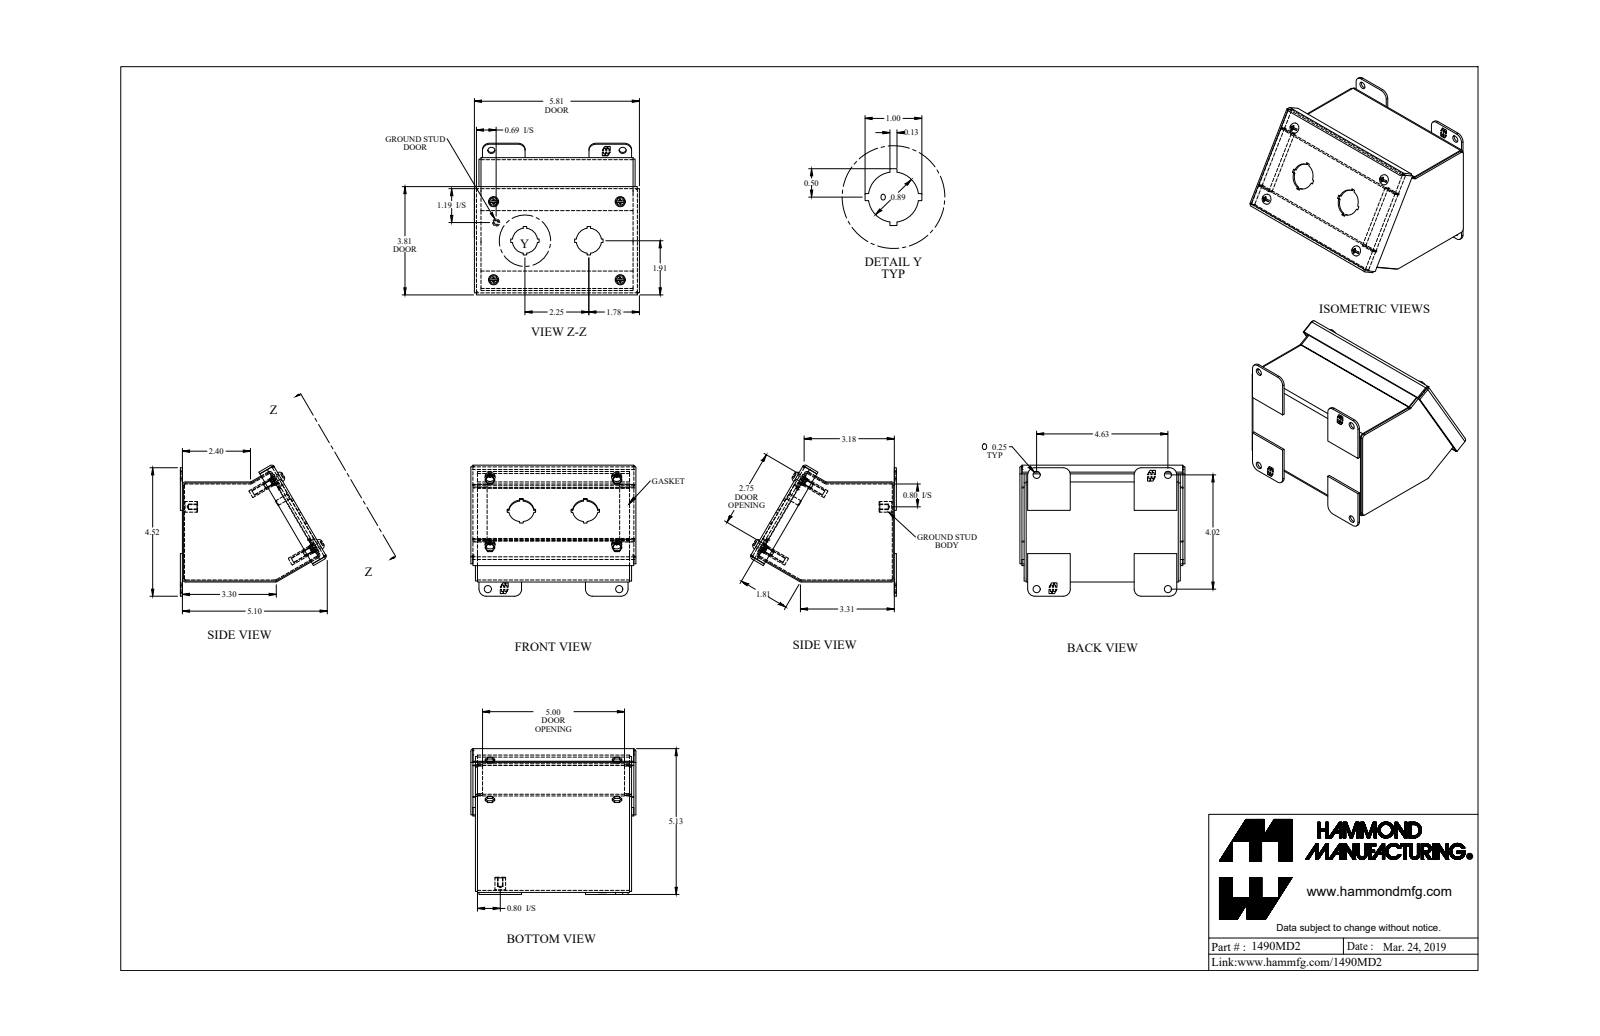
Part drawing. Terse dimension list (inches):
name: 1490MD2_Default
written by: SolidWorks 2019 (CONFIG_CONTROL_DESIGN)
unit: in
bodies: 21 solids, 628 faces (442 planar, 148 cylindrical, 38 other)
size: 5.812 × 5.176 × 4.635
volume: 10.04 in³; area: 290.9 in²
holes: 8× ⌀0.25, 4× ⌀0.159, 1× ⌀0.156, 1× ⌀0.875, 1× ⌀0.875
bosses: 4× ⌀0.39, 4× ⌀0.275, 4× ⌀0.19, 4× ⌀0.148, 1× ⌀0.375
rounds: 18× R0.108, 12× R0.036, 8× R0.25, 4× R0.125, 4× R0.16, 4× R0.171
face distances: 0.072, 5.428, 3.45, 5.356, 5.5, 3.522, 3.378, 0.144, 3.428, 0.221
hole spacings: 4.46, 4.474, 1.764, 2.746, 2.75, 2.751, 2.755, 3.626
